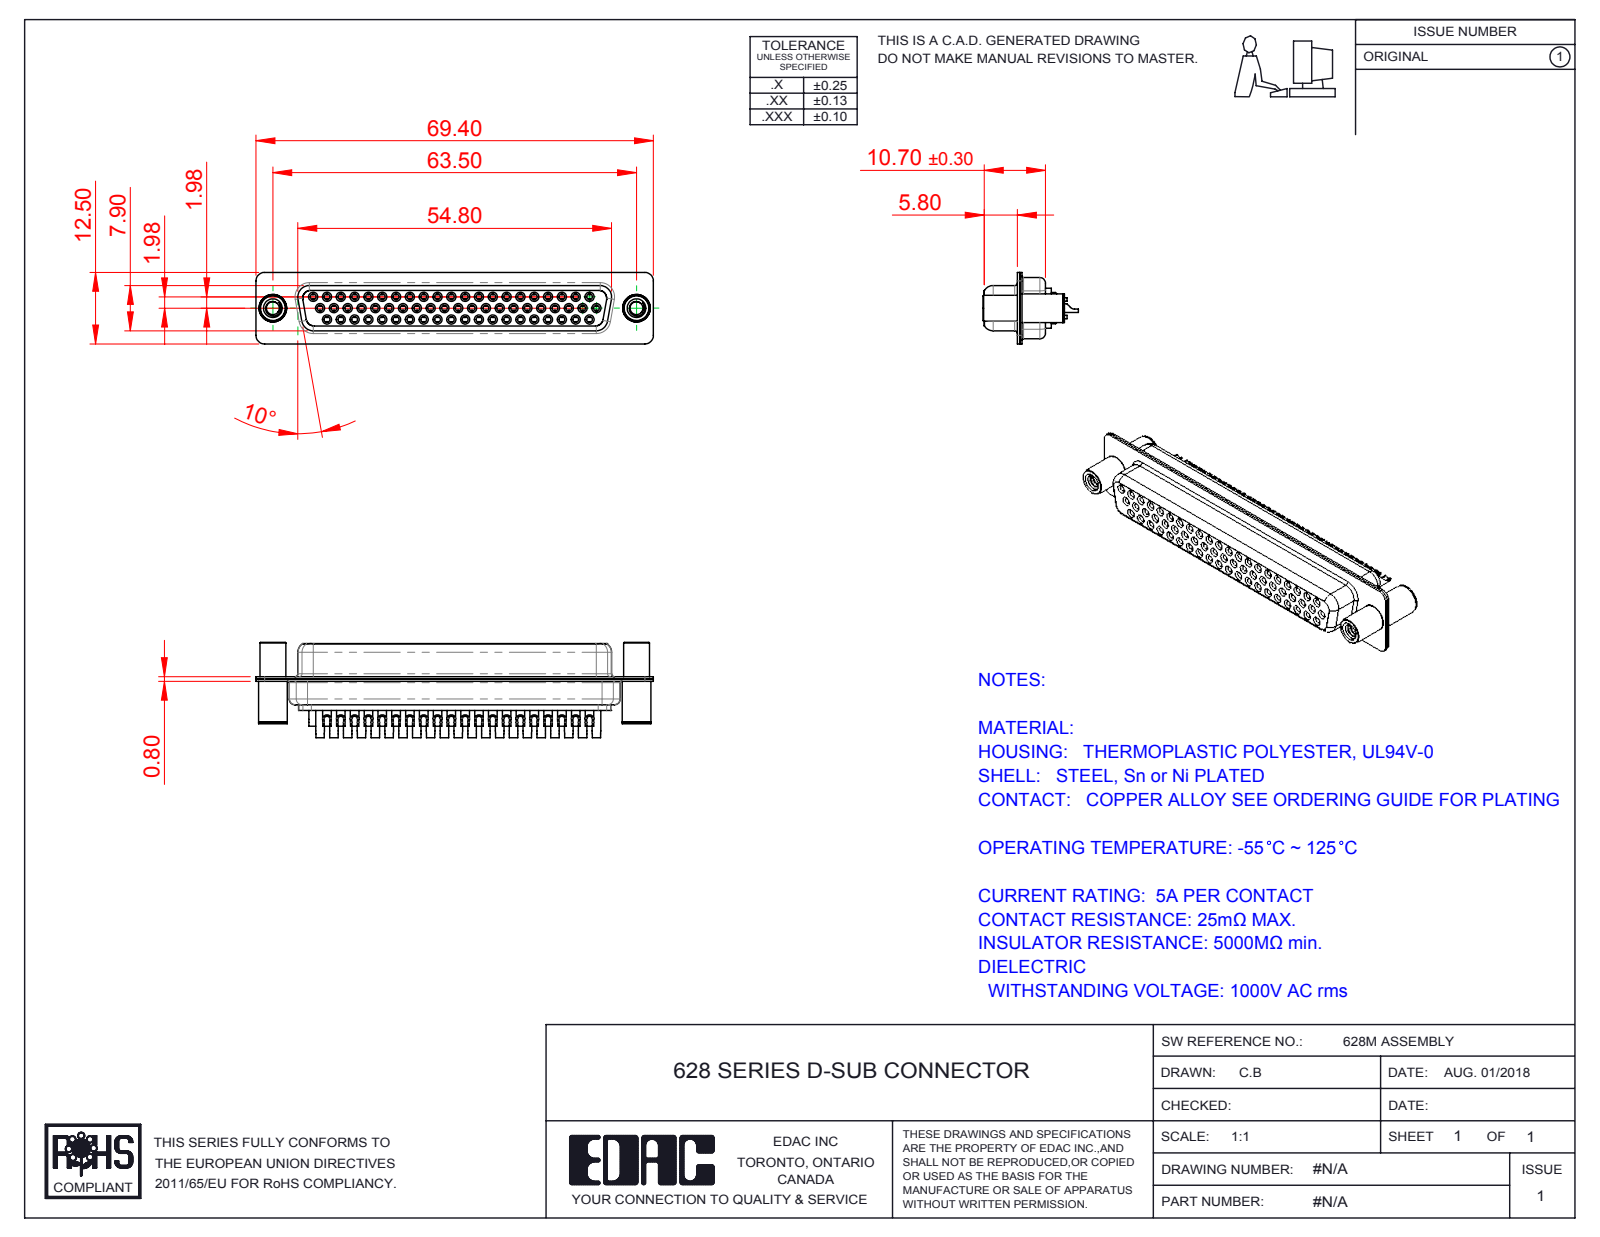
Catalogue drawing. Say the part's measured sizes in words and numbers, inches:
The part is named "638M Contact Row 1_32; 638M Shell Rear_62 Contacts; 638M Contact Row 2_32; 638M Housing_62 Contacts (+4 more)". Its 3-D file was written by "SolidWorks 2020 (CONFIG_CONTROL_DESIGN)". It is 67 solids with 3775 faces: 1127 planar, 1491 cylindrical and 1157 other. Overall it measures 2.732 by 0.656 by 0.492 inches. Its volume is 0.327 cubic inches and its surface area 26.97 square inches. Round holes: 62 of diameter 0.039, 62 of diameter 0.043, 62 of diameter 0.067, 62 of diameter 0.071, 62 of diameter 0.079, 2 of diameter 0.089, 2 of diameter 0.128, 2 of diameter 0.157, 2 of diameter 0.189. Round bosses or shafts: 62 of diameter 0.087, 62 of diameter 0.063, 62 of diameter 0.059, 2 of diameter 0.197, 2 of diameter 0.193, 2 of diameter 0.177. Partial cylindrical surfaces (rounded edges, fillets, slot ends): 16 of radius 0.059, 12 of radius 0.079, 8 of radius 0.053, 8 of radius 0.063, 7 of radius 0.039, 4 of radius 0.01, 4 of radius 0.02, 4 of radius 0.024. The main face-to-face distances are 0.016, 0.055, 0.018, 0.333, 0.35, 0.071, 0.039, 0.244, 0.278, 0.073. The hole center spacings are 0.285, 0.091, 0.095, 0.163, 0.38, 0.19, 0.57, 0.665.
